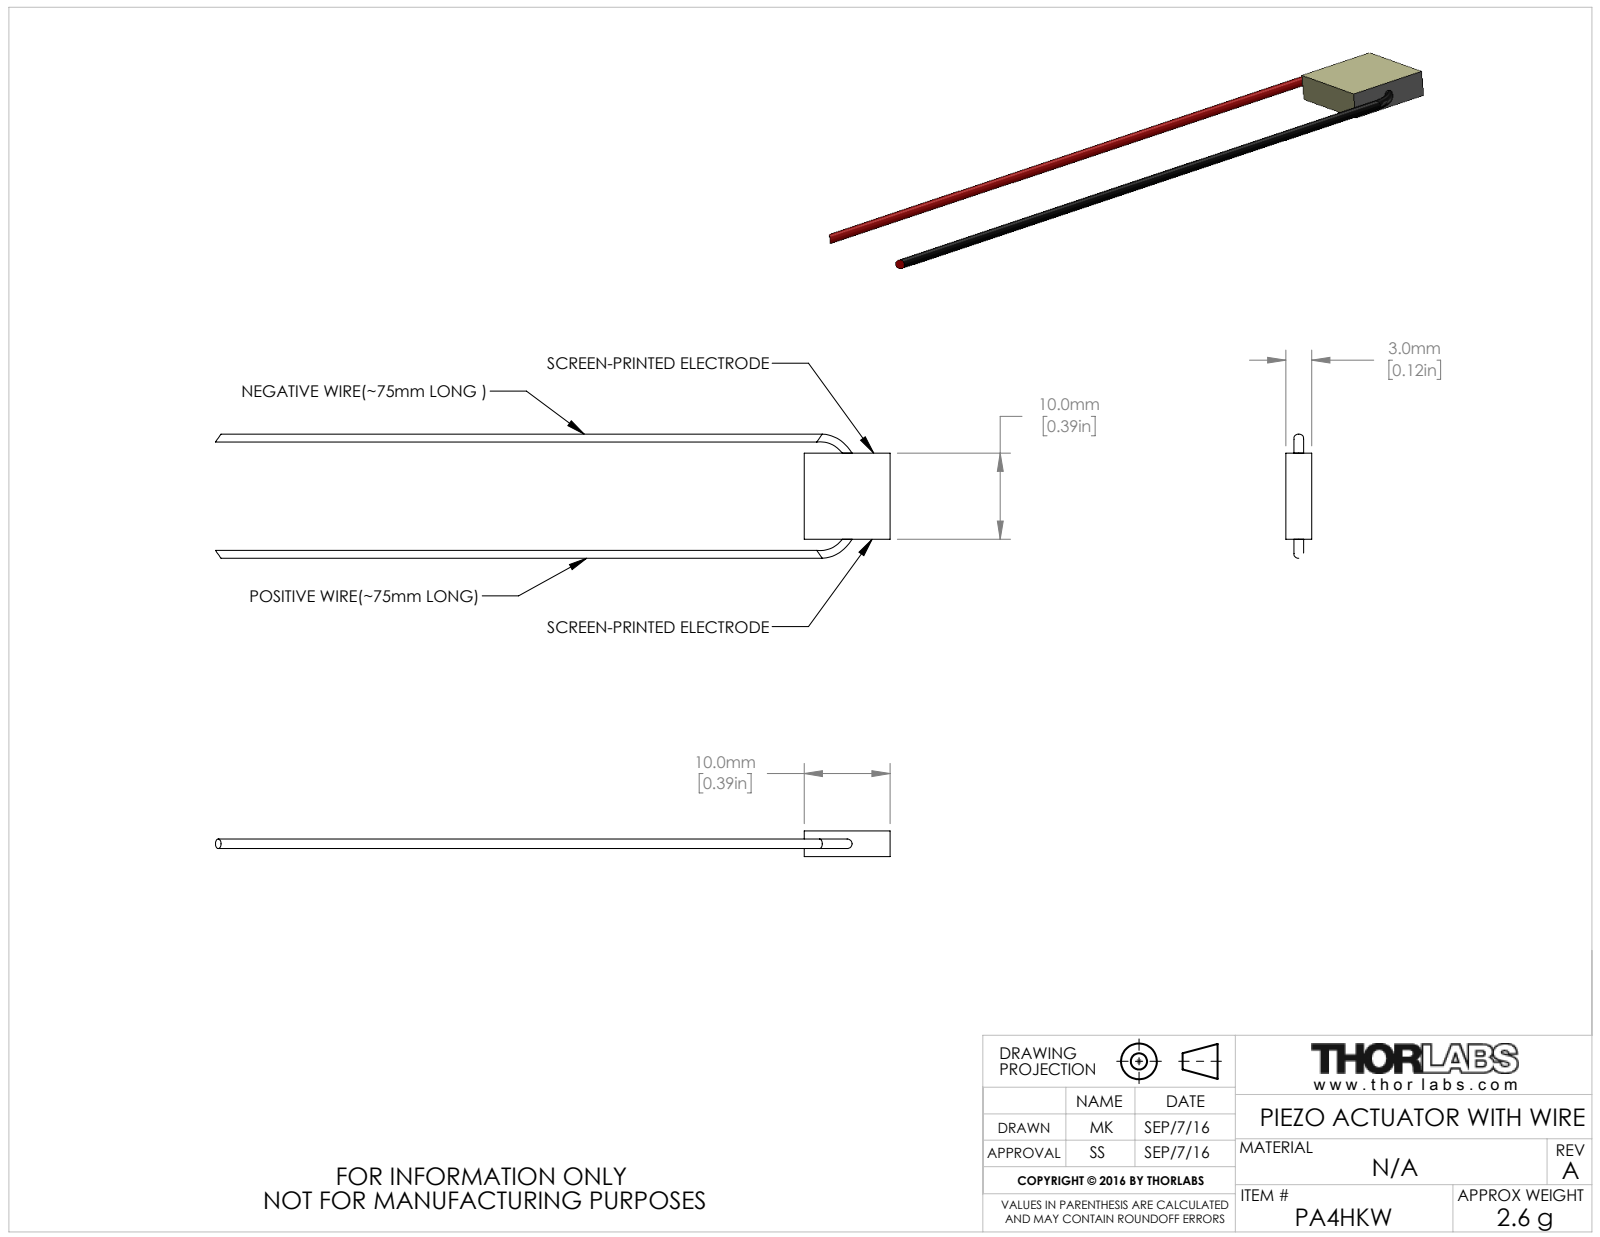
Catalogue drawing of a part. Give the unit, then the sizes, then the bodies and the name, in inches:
Units: inches
Overall size (bounding box): 3.093 × 0.569 × 0.118
Main face-to-face distances: 0.118, 0.394
Volume: 0.026 in³ · Surface area: 1.24 in²
Bodies: 3 solids, 18 faces (10 planar, 0 cylindrical, 8 other)
Part name (STEP PRODUCT): CTN003180
STEP written by: SolidWorks 2016 (AUTOMOTIVE_DESIGN)
